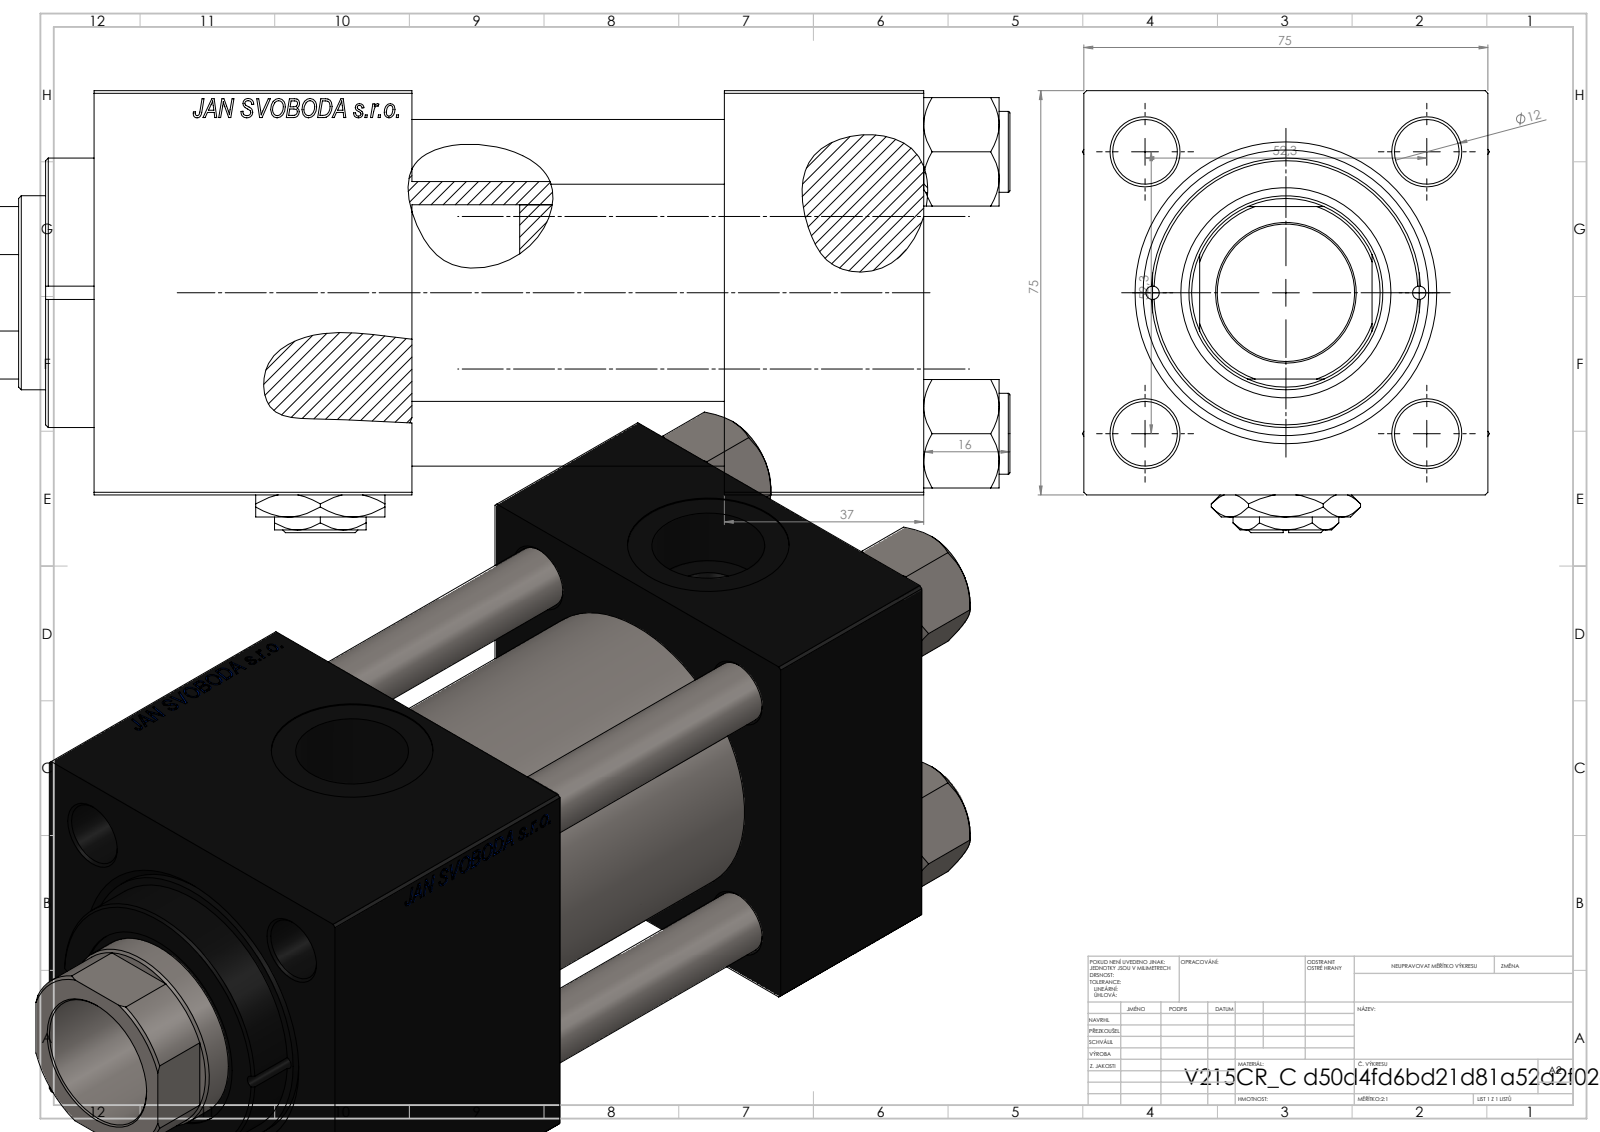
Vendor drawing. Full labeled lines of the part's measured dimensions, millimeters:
Part name (STEP PRODUCT): V215_VC_A; Zatka_pro_OIL_PORT; V215CR_C_Body; V215CR_C_TYCINKA (+2 more)
STEP written by: SolidWorks 2019 (CONFIG_CONTROL_DESIGN)
Units: millimetres
Bodies: 12 solids, 1202 faces (551 planar, 95 cylindrical, 556 other)
Overall size (bounding box): 195 × 82 × 75.54
Volume: 682 376 mm³ · Surface area: 157 588 mm²
Round holes (diameter × count): ⌀12 ×4, ⌀2.5 ×2, ⌀7 ×2, ⌀20.96 ×2, ⌀30 ×2, ⌀25.5 ×1, ⌀36 ×1, ⌀39 ×1, ⌀41 ×1, ⌀53 ×1
Round bosses / shafts (diameter × count): ⌀15 ×4, ⌀56 ×1, ⌀50 ×1
Partial cylindrical surfaces — rounded edges, fillets, slot ends (radius × count): R17.5 ×1
Main face-to-face distances: 75, 37, 95, 58, 59, 154, 117, 125.3, 88.3, 30.3
Hole centre spacings: 26.19, 36.98, 52.3, 57.22, 24.75, 73.96, 49.5, 93.5
